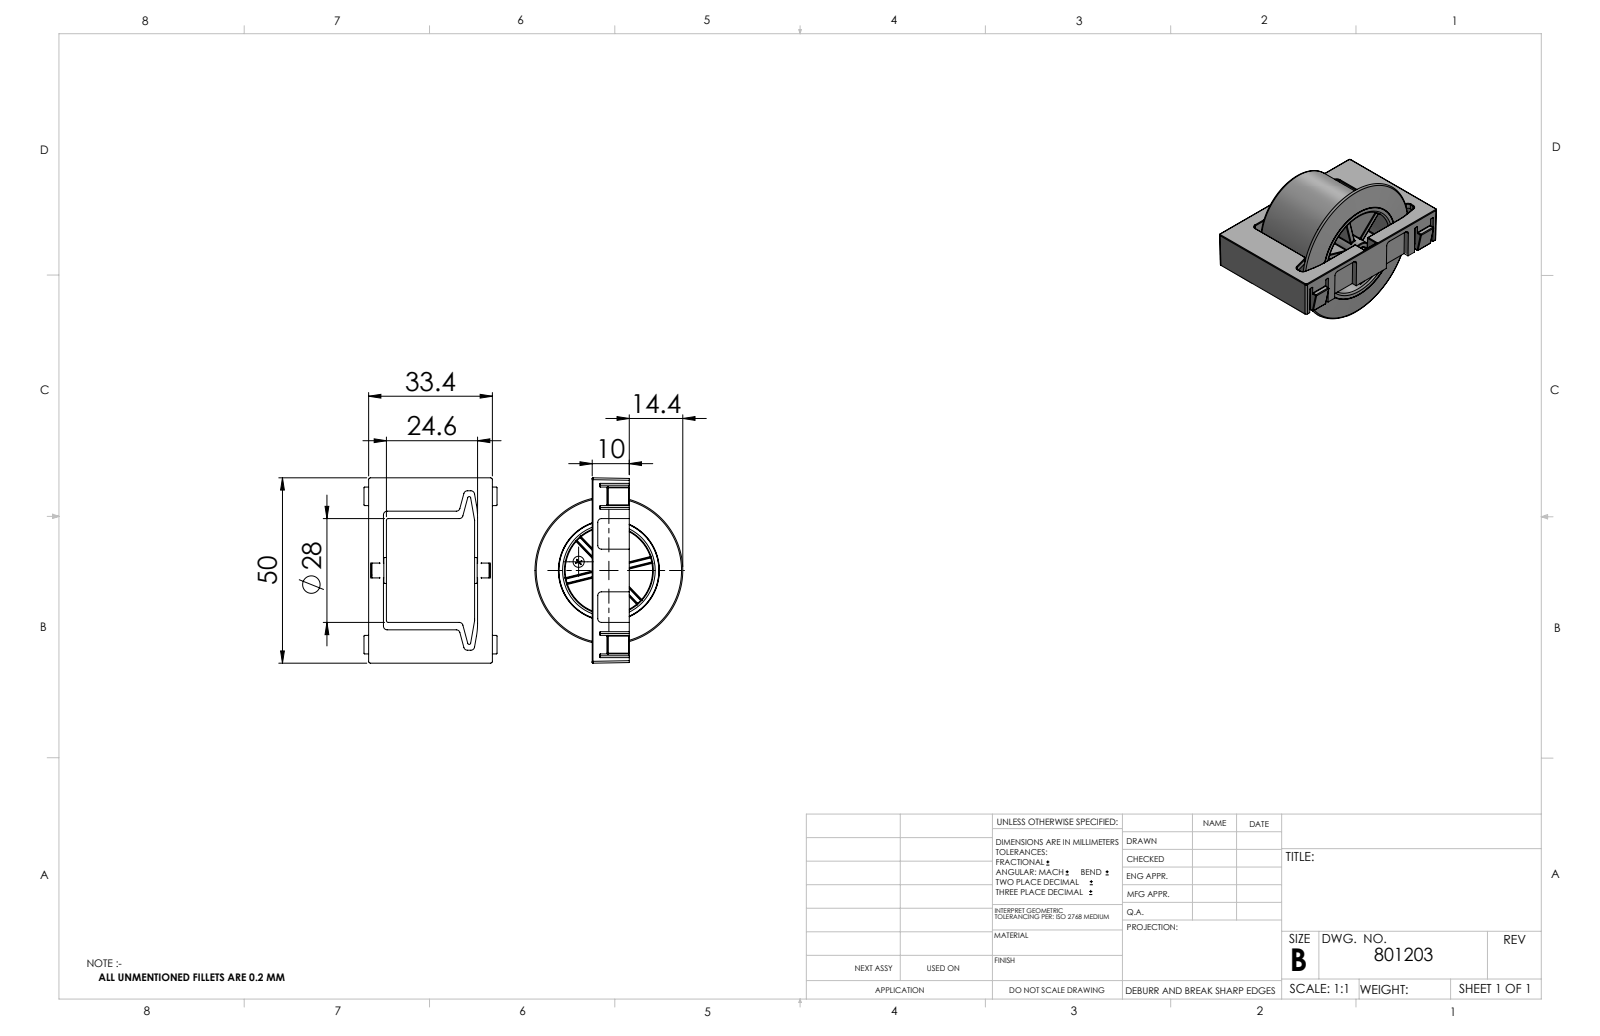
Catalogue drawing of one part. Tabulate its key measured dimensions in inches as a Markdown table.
| quantity | value |
| --- | --- |
| part name | 801203_c_1 |
| STEP written by | SolidWorks 2014 (CONFIG_CONTROL_DESIGN) |
| units | inches |
| bodies | 3 solids, 806 faces (172 planar, 291 cylindrical, 343 other) |
| overall size | 1.968 × 1.57 × 1.413 |
| volume | 0.783 in³ |
| surface area | 21.81 in² |
| round holes (diameter × count) | 0.165 × 1, 0.945 × 1 |
| round bosses / shafts (diameter × count) | 1.102 × 1, 0.276 × 1, 0.198 × 1, 0.157 × 1, 0.118 × 1 |
| partial cylindrical surfaces (radius × count) | 0.008 × 159, 0.02 × 22, 0.039 × 12, 0.004 × 2, 0.787 × 2, 0.081 × 1 |
| main face-to-face distances | 0.059, 0.465, 0.535, 0.071, 0.394, 0.059, 1, 0.583, 0.335, 0.079 |
